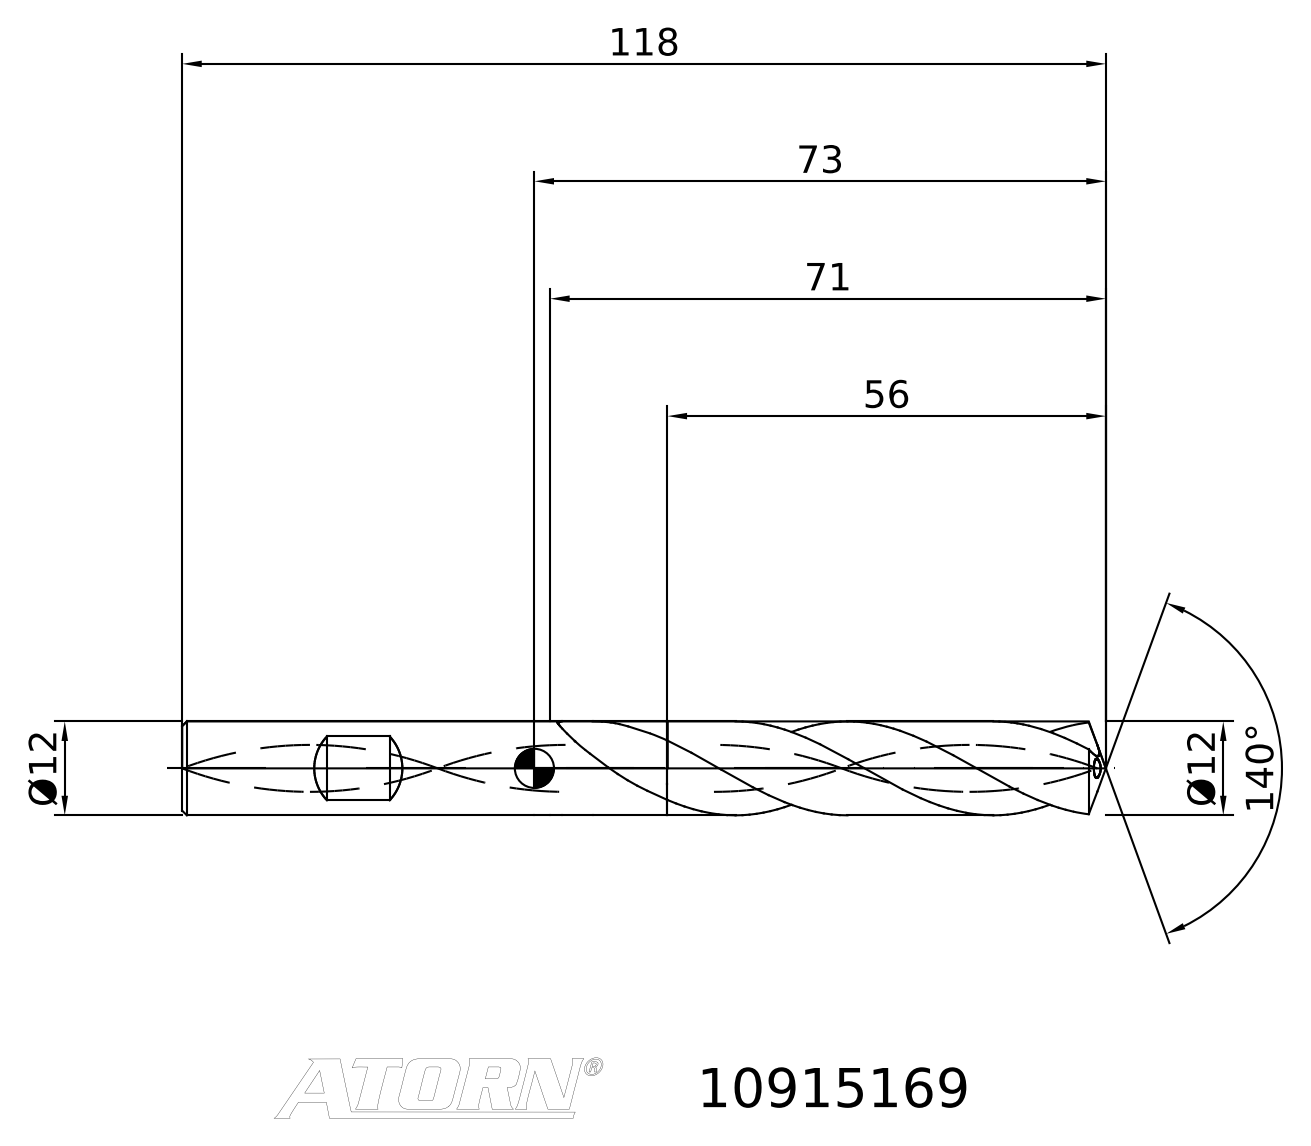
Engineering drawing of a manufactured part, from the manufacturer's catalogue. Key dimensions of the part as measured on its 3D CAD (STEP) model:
STEP written by: TDM (AUTOMOTIVE_DESIGN)
Units: millimetres
Bodies: 2 solids, 33 faces (8 planar, 0 cylindrical, 25 other)
Overall size (bounding box): 118 × 14.05 × 12.05
Volume: 10 564 mm³ · Surface area: 4 946 mm²
Main face-to-face distances: 62, 54.36, 116.36
